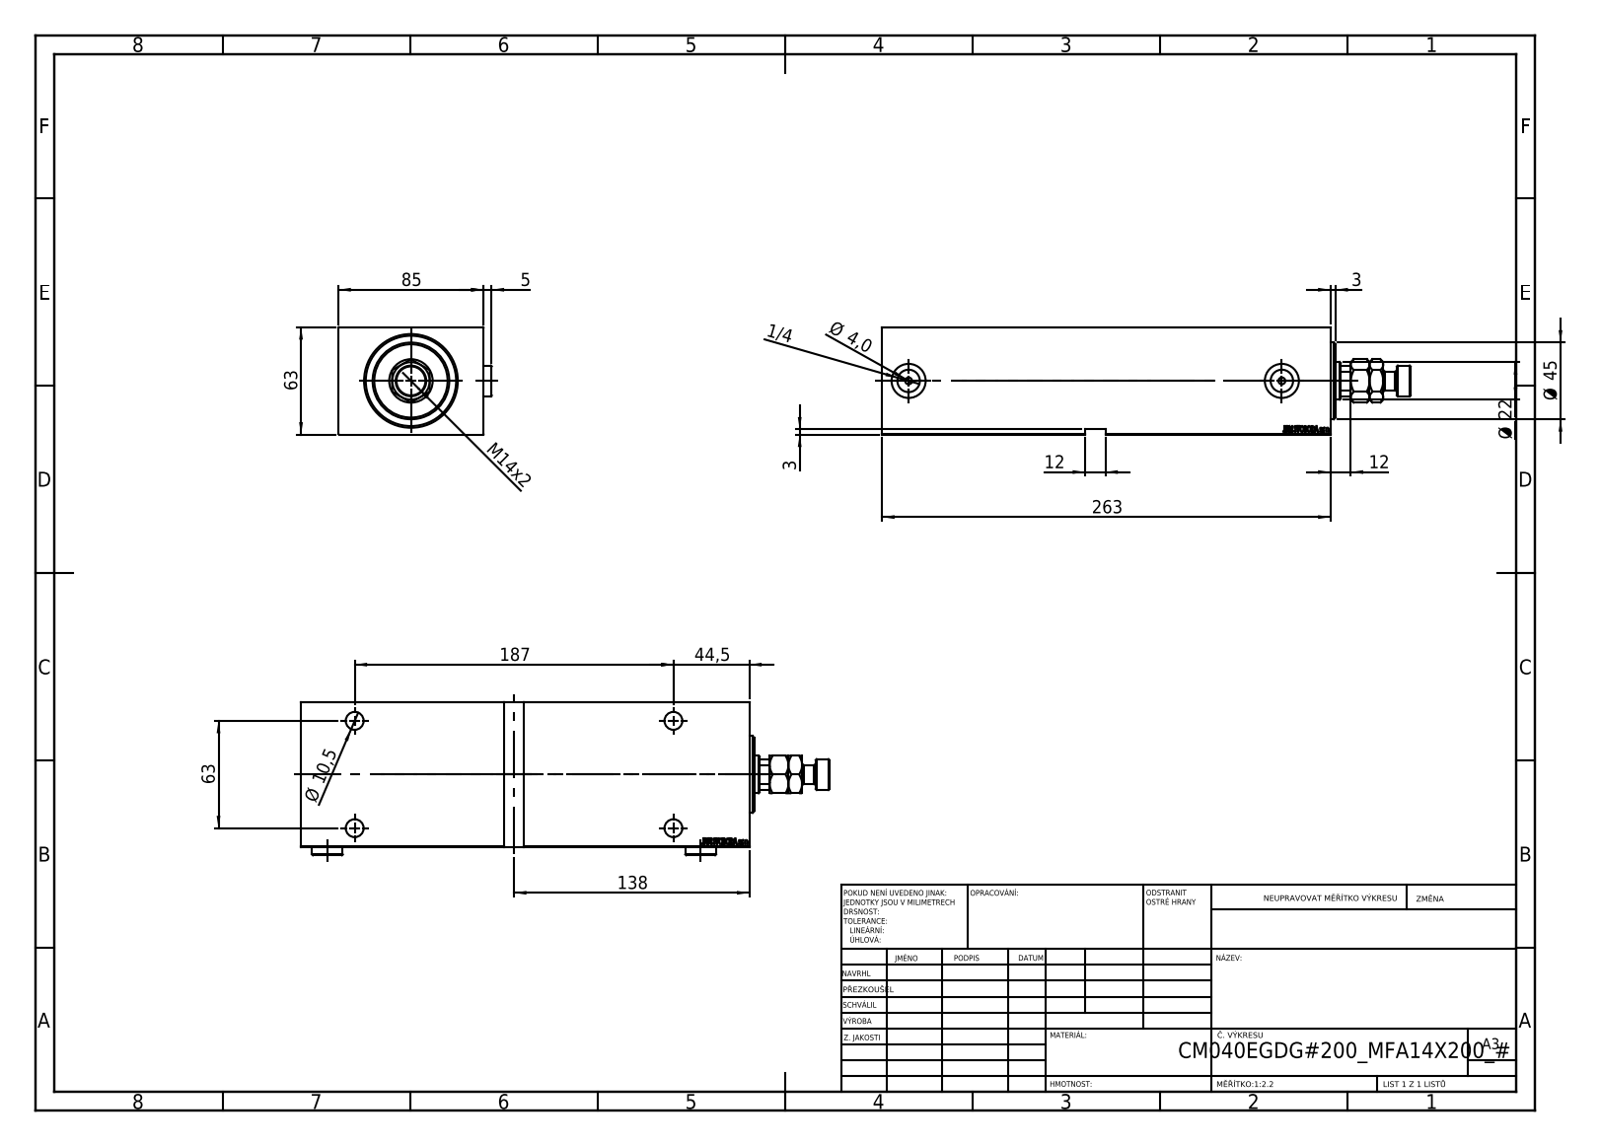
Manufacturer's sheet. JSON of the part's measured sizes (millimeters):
{"part_name": "V450CM_VC_B; MFA; V450CM_E_Body; Zatka_OIL_PORT (+1 more)", "step_written_by": "SolidWorks 2019 (CONFIG_CONTROL_DESIGN)", "units": "millimeters", "bodies": {"solids": 6, "faces": 964, "planar": 462, "cylindrical": 72, "other": 430}, "overall_size": [310, 89.9, 63], "volume_mm3": 1215000, "surface_area_mm2": 168291, "round_holes": [[10.5, 4], [16.5, 4], [4, 2], [13.16, 2], [20, 2], [12.5, 1], [22, 1], [25.5, 1], [40, 1], [53, 1]], "round_bosses_or_shafts": [[18, 3], [45, 1], [42, 1], [11, 1]], "partial_cylinders_radius": [[10.5, 1]], "face_to_face_distances": [63, 85, 263, 12, 251, 5, 3, 246, 258, 84.9], "hole_center_spacings": [63, 187, 197.33, 219]}
